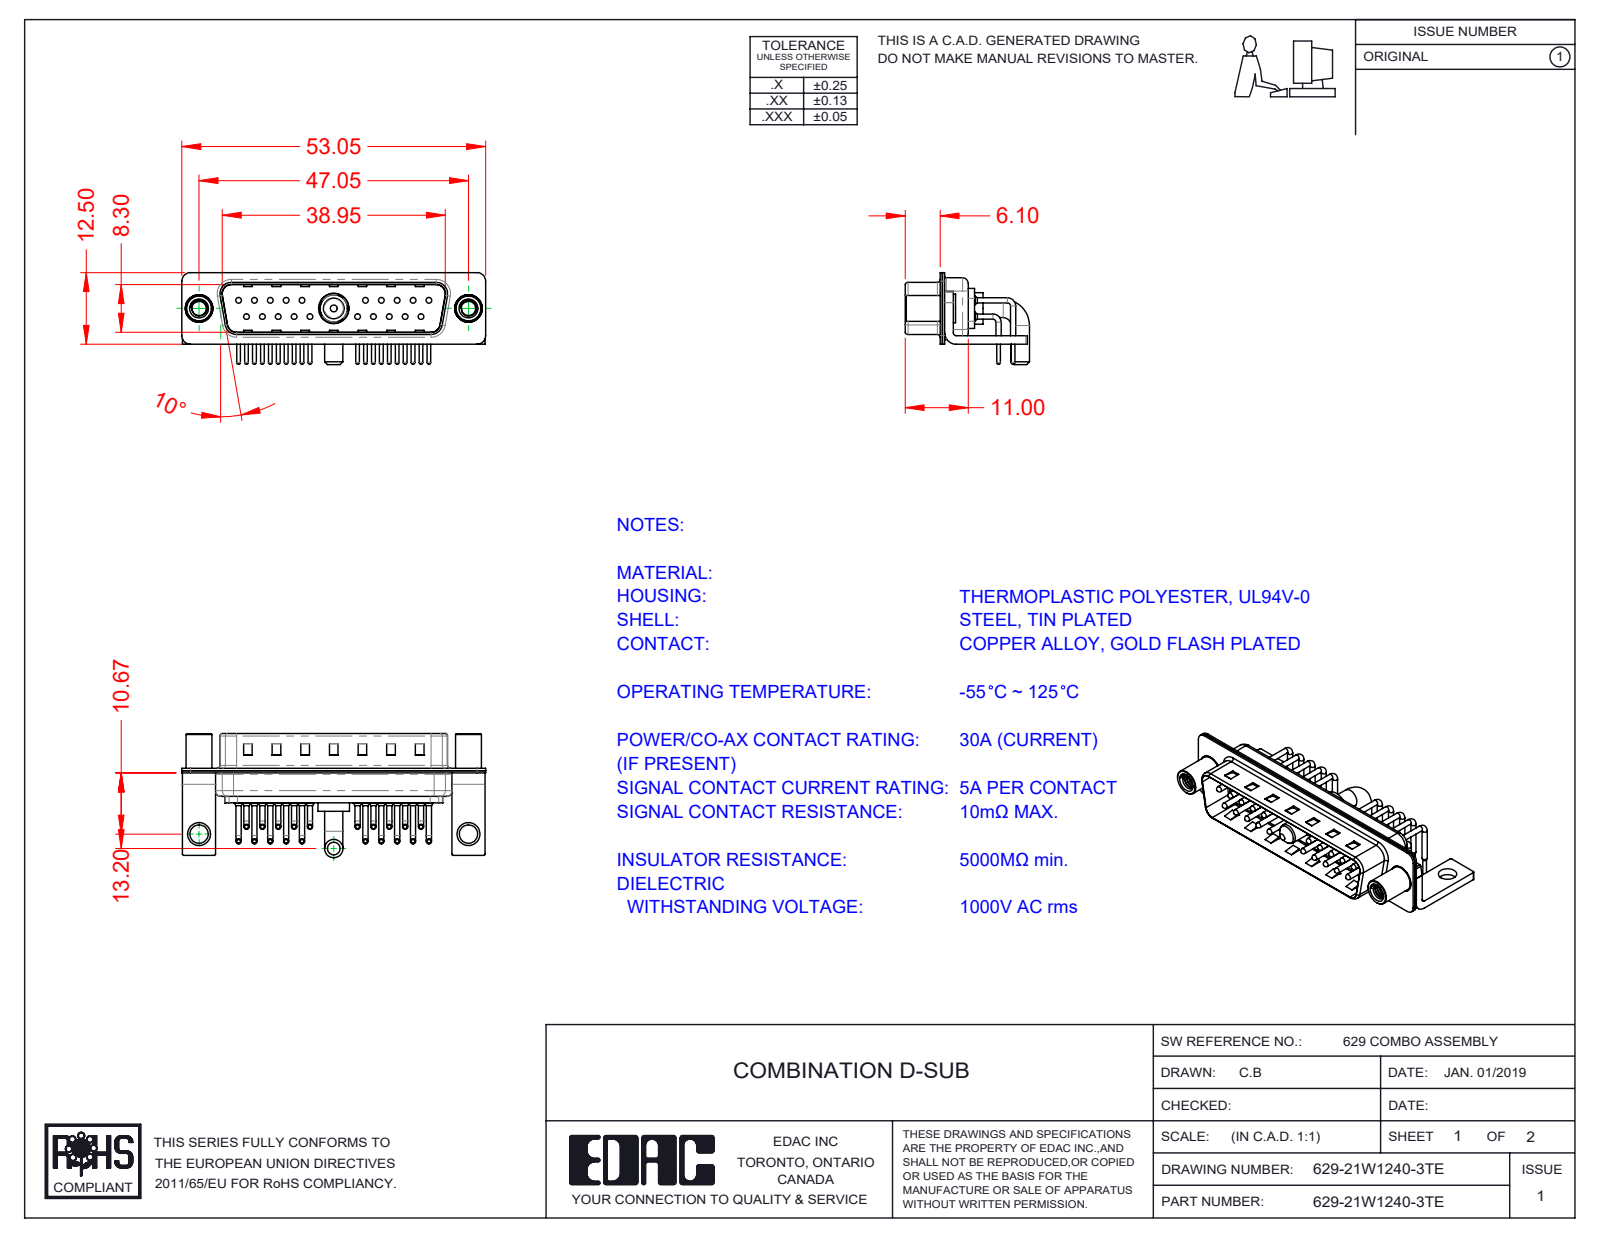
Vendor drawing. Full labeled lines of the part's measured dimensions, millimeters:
Part name (STEP PRODUCT): 629-21W1240-3TE; 629Combo Shell Front_25 Contacts; 629Combo Contact Row 1; 629Combo Stabilizer Bracket (+5 more)
STEP written by: SolidWorks 2020 (CONFIG_CONTROL_DESIGN)
Units: millimetres
Bodies: 29 solids, 2717 faces (1483 planar, 950 cylindrical, 284 other)
Overall size (bounding box): 53.05 × 21.7 × 16.05
Volume: 3 430 mm³ · Surface area: 8 538 mm²
Round holes (diameter × count): ⌀0.75 ×20, ⌀1.6 ×20, ⌀2 ×20, ⌀2.5 ×2, ⌀3.2 ×2, ⌀4 ×2, ⌀4.8 ×2, ⌀4.85 ×1, ⌀5.3 ×1
Round bosses / shafts (diameter × count): ⌀0.9 ×40, ⌀1.5 ×20, ⌀1 ×20, ⌀0.65 ×20, ⌀5 ×2, ⌀4.9 ×2, ⌀4.5 ×2, ⌀3.2 ×2
Partial cylindrical surfaces — rounded edges, fillets, slot ends (radius × count): R1.01 ×20, R0.25 ×16, R1.5 ×16, R2 ×13, R0.5 ×9, R1.6 ×8, R0.6 ×4, R0.65 ×4
Main face-to-face distances: 0.4, 0.8, 9.5, 1.5, 9.1, 8.7, 9.9, 0.6, 2.1, 0.75
Hole centre spacings: 3.16, 2.77, 5.54, 8.31, 5.04, 19.39, 20.97, 22.16
